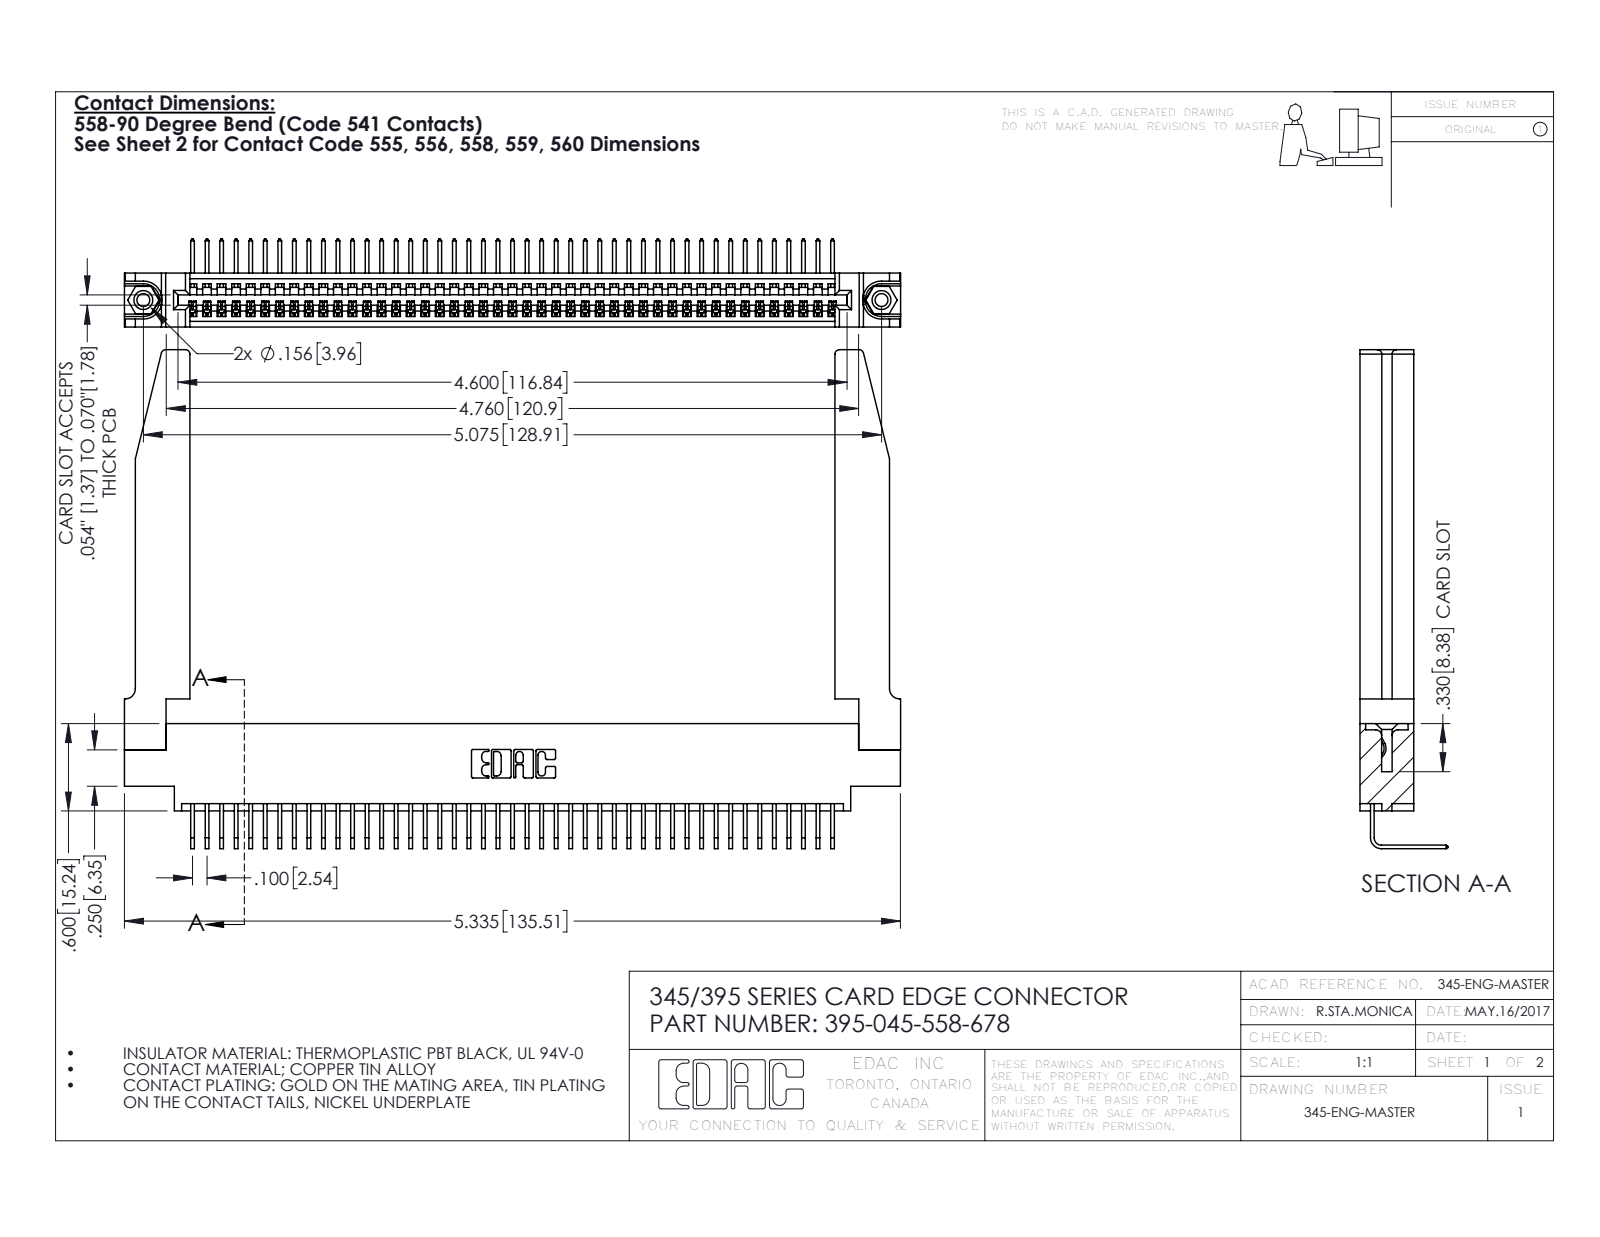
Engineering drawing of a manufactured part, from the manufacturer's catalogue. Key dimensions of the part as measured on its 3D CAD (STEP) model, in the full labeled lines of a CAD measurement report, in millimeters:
Part name (STEP PRODUCT): 345 Part_0.170 Offset - 0.156 Dia-TH; 345-292-001_558 Tail - 2; 345-250-001_345-250-001-102; 395-045-558-678 (+1 more)
STEP written by: SolidWorks 2016 (CONFIG_CONTROL_DESIGN)
Units: millimetres
Bodies: 50 solids, 3064 faces (2116 planar, 896 cylindrical, 52 other)
Overall size (bounding box): 135.5 × 87.1 × 15.4
Volume: 20 700 mm³ · Surface area: 25 080 mm²
Round holes (diameter × count): ⌀2.3 ×2, ⌀3.2 ×2, ⌀4 ×2, ⌀1.6 ×1
Round bosses / shafts (diameter × count): ⌀3.9 ×2
Partial cylindrical surfaces — rounded edges, fillets, slot ends (radius × count): R0.2 ×90, R0.3 ×22, R0.8 ×8, R0.2 ×6, R0.8 ×6, R0.7 ×3, R0.8 ×2, R1 ×2
Main face-to-face distances: 9.4, 1.8, 7.6, 2.5, 6.9, 0.6, 5.1, 5.7, 3.8, 3.8
Hole centre spacings: 6.9, 122.9, 128.9
